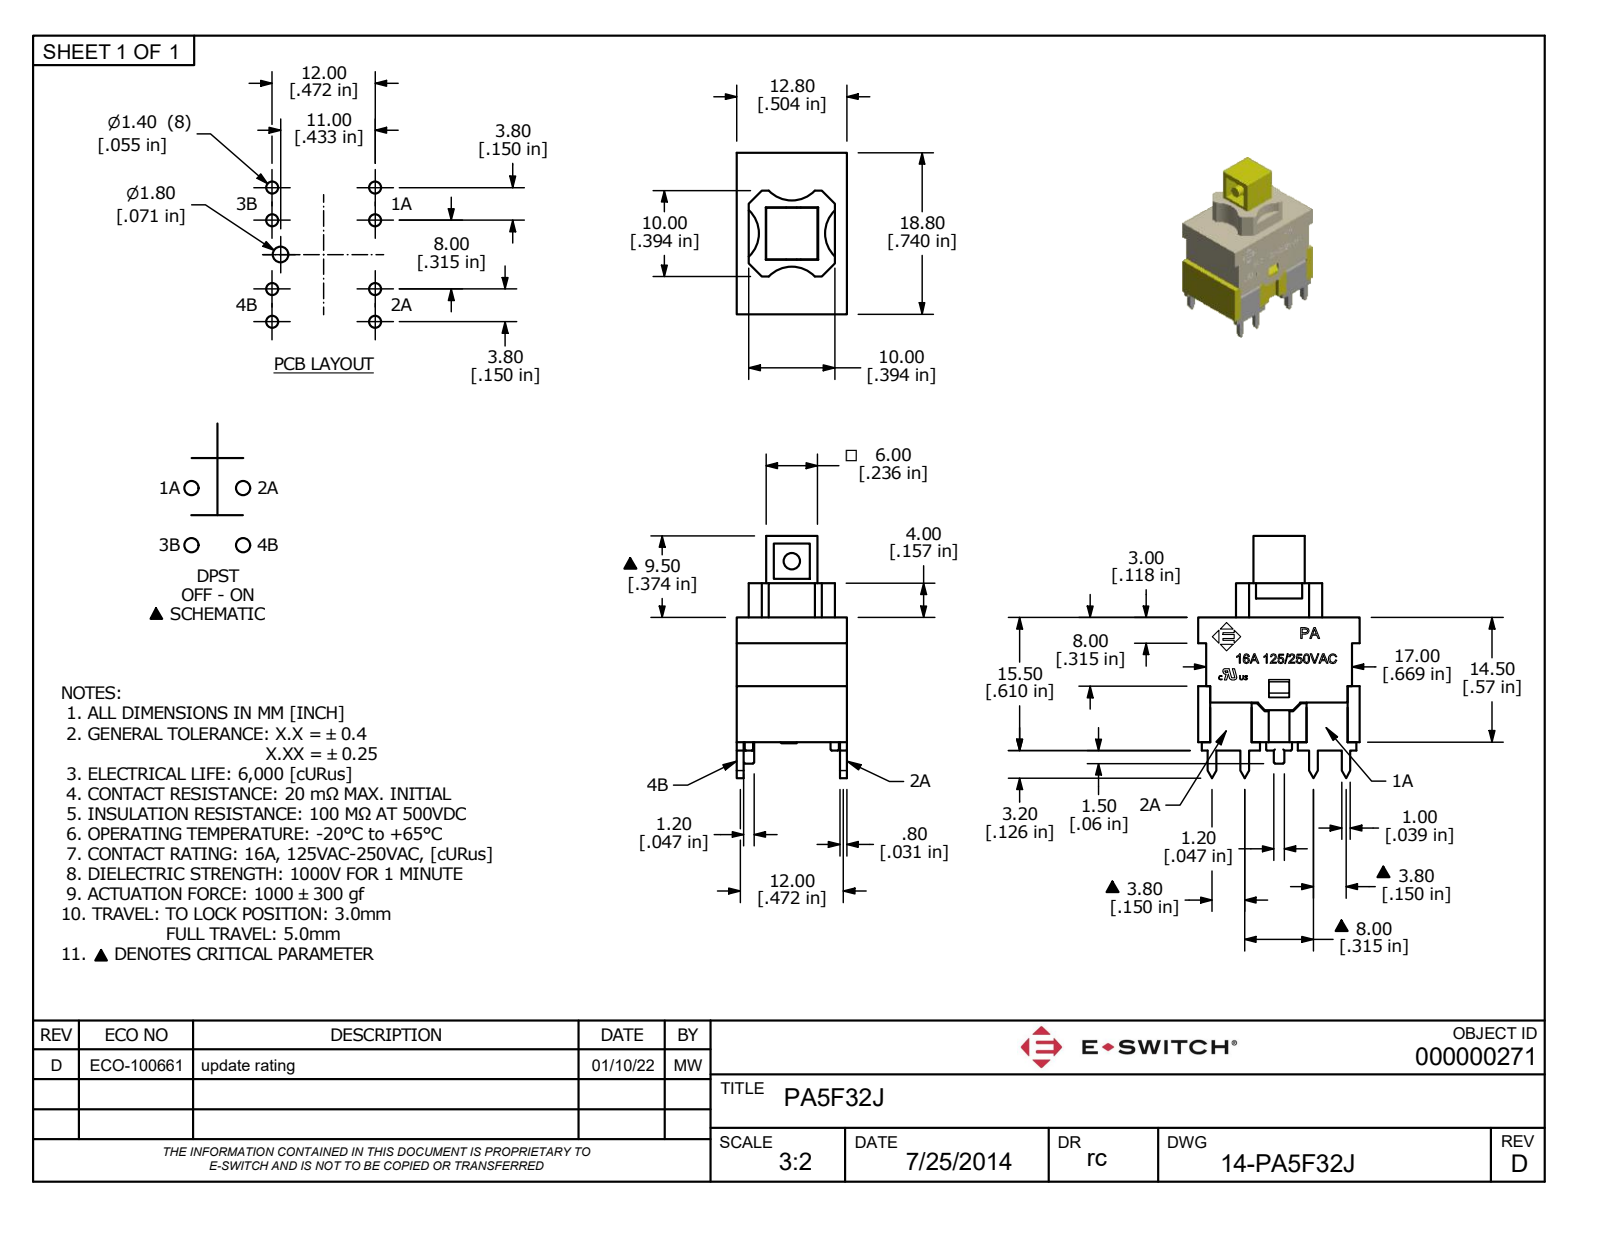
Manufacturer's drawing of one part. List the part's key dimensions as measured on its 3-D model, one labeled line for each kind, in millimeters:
Part name (STEP PRODUCT): PA5F32J
STEP written by: Autodesk Inventor 2022 (AUTOMOTIVE_DESIGN)
Units: millimetres
Bodies: 1 solid, 855 faces (642 planar, 82 cylindrical, 131 other)
Overall size (bounding box): 28.2 × 18.8 × 12.8
Volume: 2 142 mm³ · Surface area: 4 317 mm²
Round holes (diameter × count): ⌀1.2 ×2, ⌀3 ×1
Round bosses / shafts (diameter × count): ⌀0.95 ×4, ⌀2.5 ×2, ⌀1.9 ×1
Partial cylindrical surfaces — rounded edges, fillets, slot ends (radius × count): R0.25 ×22, R0.12 ×16, R0.15 ×8, R1 ×5, R3.71 ×4, R0.5 ×1, R0.6 ×1, R1.79 ×1
Main face-to-face distances: 0.8, 12, 0.9, 16.8, 12.8, 2, 5.5, 8.6, 1.1, 4.4
Hole centre spacings: 11.8
